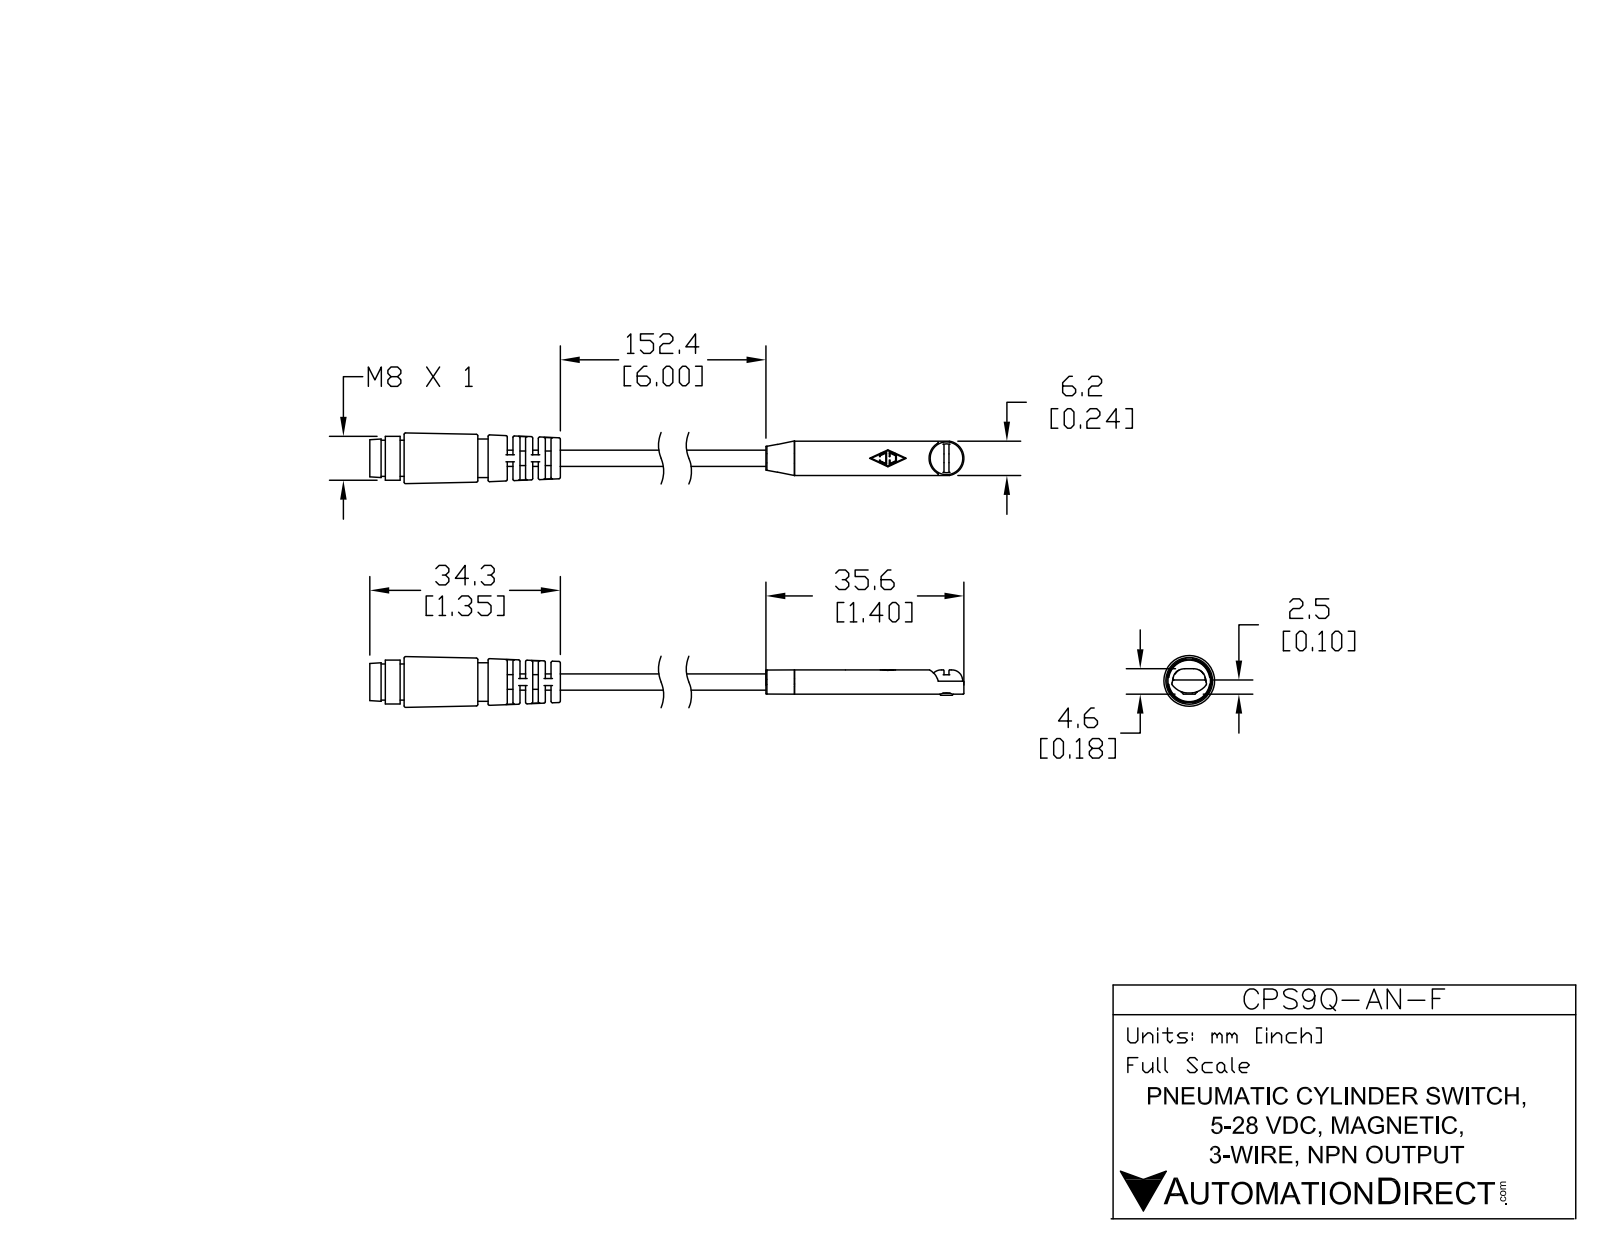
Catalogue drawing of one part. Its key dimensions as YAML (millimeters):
part_name: "CPS9Q-AN-F"
step_written_by: "SolidWorks 2014 (AUTOMOTIVE_DESIGN)"
units: millimeters
bodies: {solids: 3, faces: 256, planar: 113, cylindrical: 64, other: 79}
overall_size: [184.9, 9.1, 9.1]
volume: 3020
surface_area: 3141
round_holes:
  - {diameter: 0.8, count: 1}
  - {diameter: 5.8, count: 1}
round_bosses_or_shafts:
  - {diameter: 1, count: 3}
  - {diameter: 7.9, count: 1}
  - {diameter: 6.9, count: 1}
  - {diameter: 6.5, count: 1}
  - {diameter: 2.9, count: 1}
  - {diameter: 2.9, count: 1}
partial_cylinders:
  - {radius: 0.1, count: 4}
  - {radius: 2, count: 3}
  - {radius: 0.6, count: 2}
  - {radius: 1.5, count: 2}
  - {radius: 1.9, count: 2}
  - {radius: 1.4, count: 1}
  - {radius: 1.8, count: 1}
  - {radius: 3.1, count: 1}
face_to_face_distances: [4.6, 1.3, 2.3, 2.3, 3.3, 1, 1, 4.4, 9.6, 8.5]
